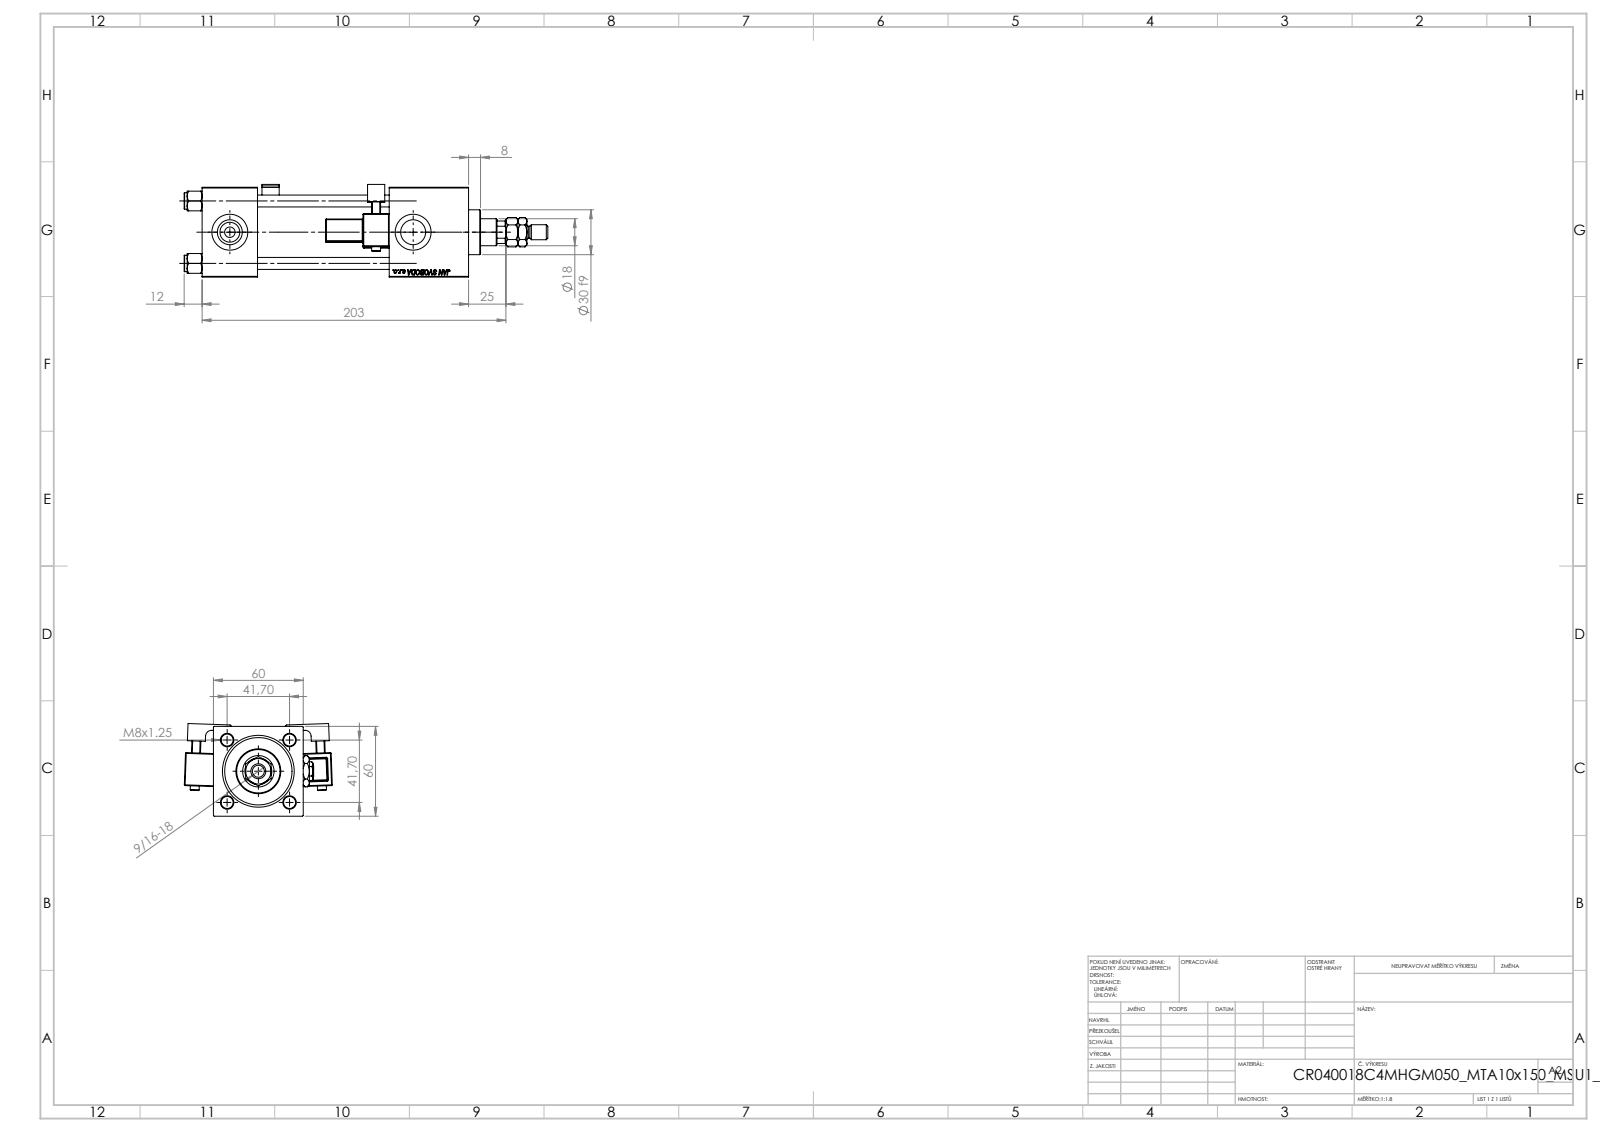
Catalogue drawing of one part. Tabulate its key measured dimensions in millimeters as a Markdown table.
| quantity | value |
| --- | --- |
| part name | MTA; V215_VC_A; V215CR_VCP_C; V215CR_C_TYCINKA (+4 more) |
| STEP written by | SolidWorks 2019 (CONFIG_CONTROL_DESIGN) |
| units | millimeters |
| bodies | 15 solids, 1399 faces (623 planar, 154 cylindrical, 622 other) |
| overall size | 243 × 98.85 × 61.9 |
| volume | 471 825 mm³ |
| surface area | 133 239 mm² |
| round holes (diameter × count) | 8 × 4, 7 × 2, 16.66 × 2, 24 × 2, 8.5 × 1, 18 × 1, 21 × 1, 31 × 1, 40 × 1, 45 × 1 |
| round bosses / shafts (diameter × count) | 11 × 4, 6 × 2, 46 × 1, 30 × 1, 10 × 1, 8 × 1 |
| partial cylindrical surfaces (radius × count) | 0.5 × 48, 1 × 2, 2.5 × 2, 4 × 2, 8.5 × 1 |
| main face-to-face distances | 60, 37, 125, 88, 53, 178, 141, 149.3, 112.3, 24.3 |
| hole center spacings | 29.49, 41.7, 58.97, 122.5 |
